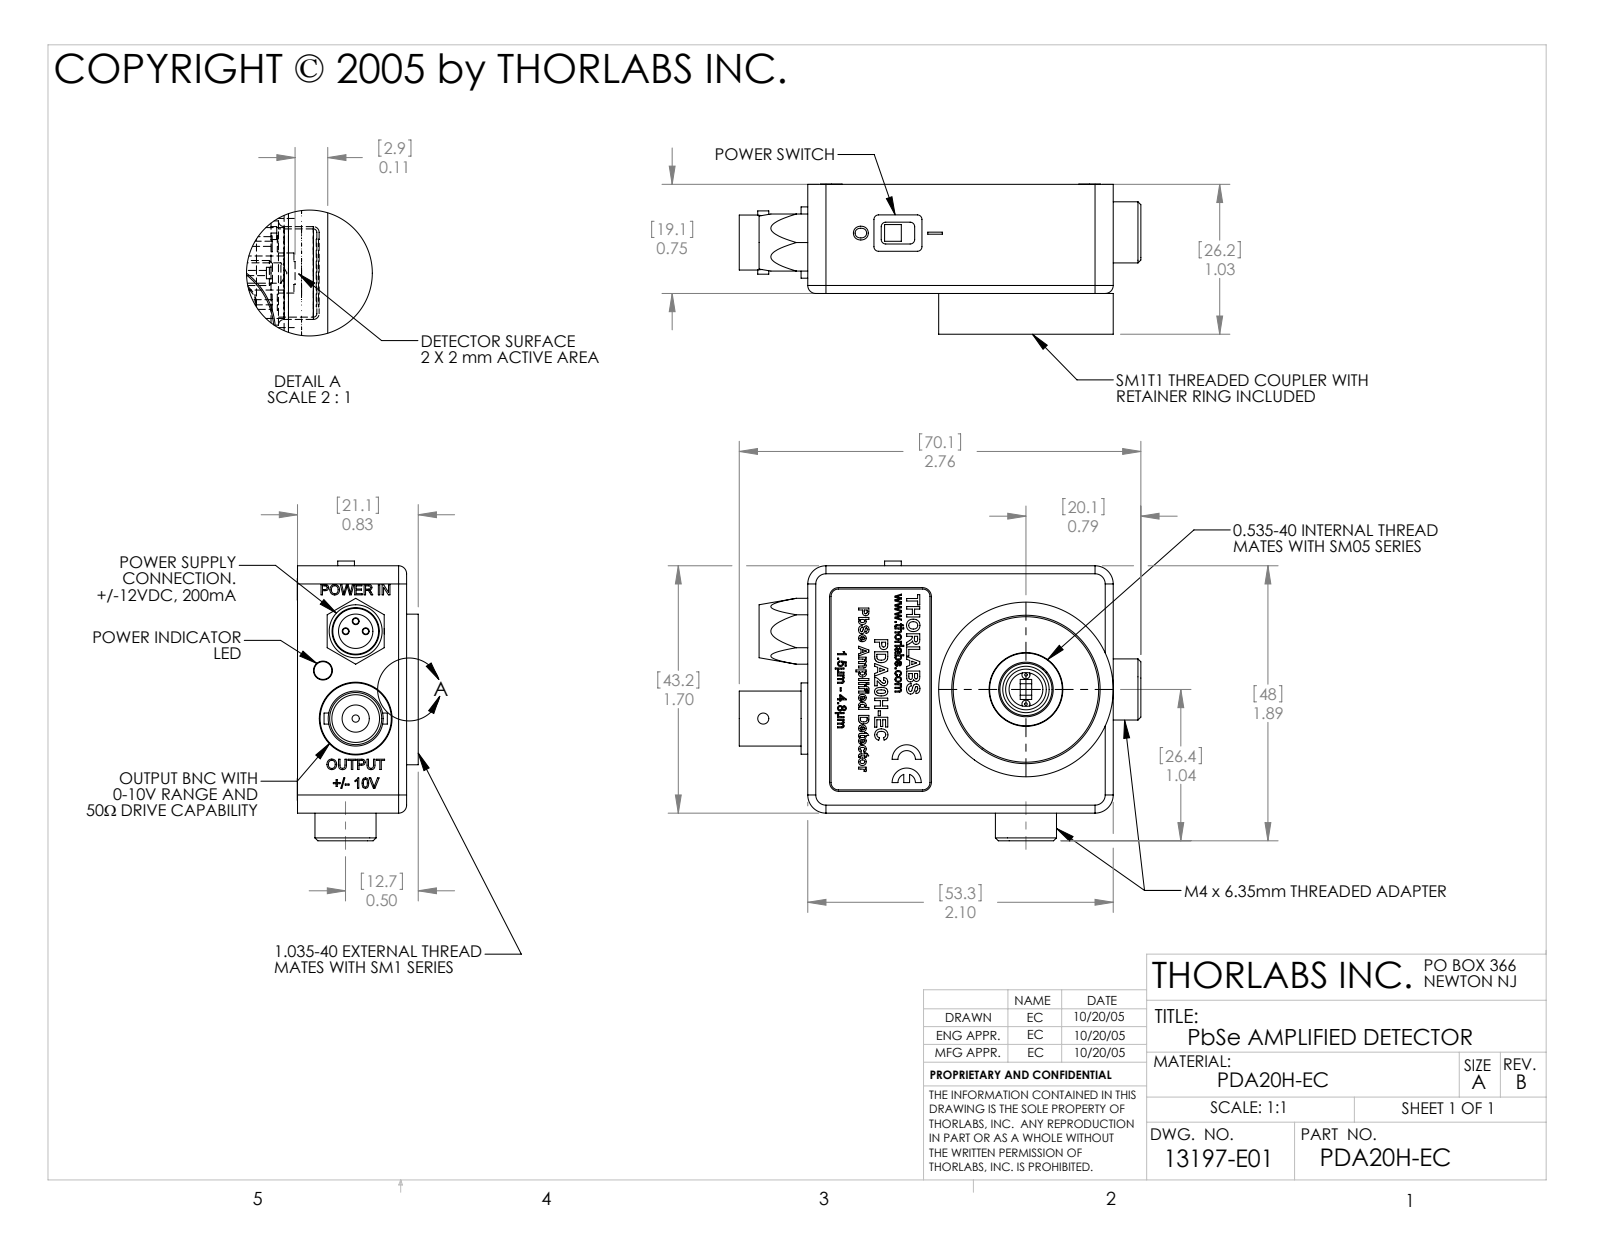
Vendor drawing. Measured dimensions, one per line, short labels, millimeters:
name: 13197-E0W
written by: SolidWorks 2009 (AUTOMOTIVE_DESIGN)
unit: mm
bodies: 17 solids, 1795 faces (984 planar, 269 cylindrical, 542 other)
size: 70.13 × 48.83 × 26.2
volume: 23 747 mm³; area: 26 781 mm²
holes: 7× ⌀1.78, 7× ⌀2.44, 4× ⌀3.17, 4× ⌀5.08, 3× ⌀0.71, 3× ⌀1, 2× ⌀1.4, 2× ⌀3.3, 2× ⌀3.81, 2× ⌀5, 1× ⌀1.27, 1× ⌀1.32
bosses: 4× ⌀3.73, 4× ⌀2.18, 3× ⌀0.45, 2× ⌀10.67, 2× ⌀5.99, 1× ⌀30.48, 1× ⌀26.29, 1× ⌀12.7
rounds: 22× R3.17, 12× R0.79, 8× R2.41, 4× R1.27, 4× R1.4, 4× R1.59, 3× R0.25, 2× R1.52
face distances: 1.59, 2.54, 13.08, 11.49, 1.27, 11.48, 9.89, 1.6, 1.78, 4.19
hole spacings: 3.6, 22.16, 1.75, 2.54, 37.1, 2.47, 2.55, 3.59
